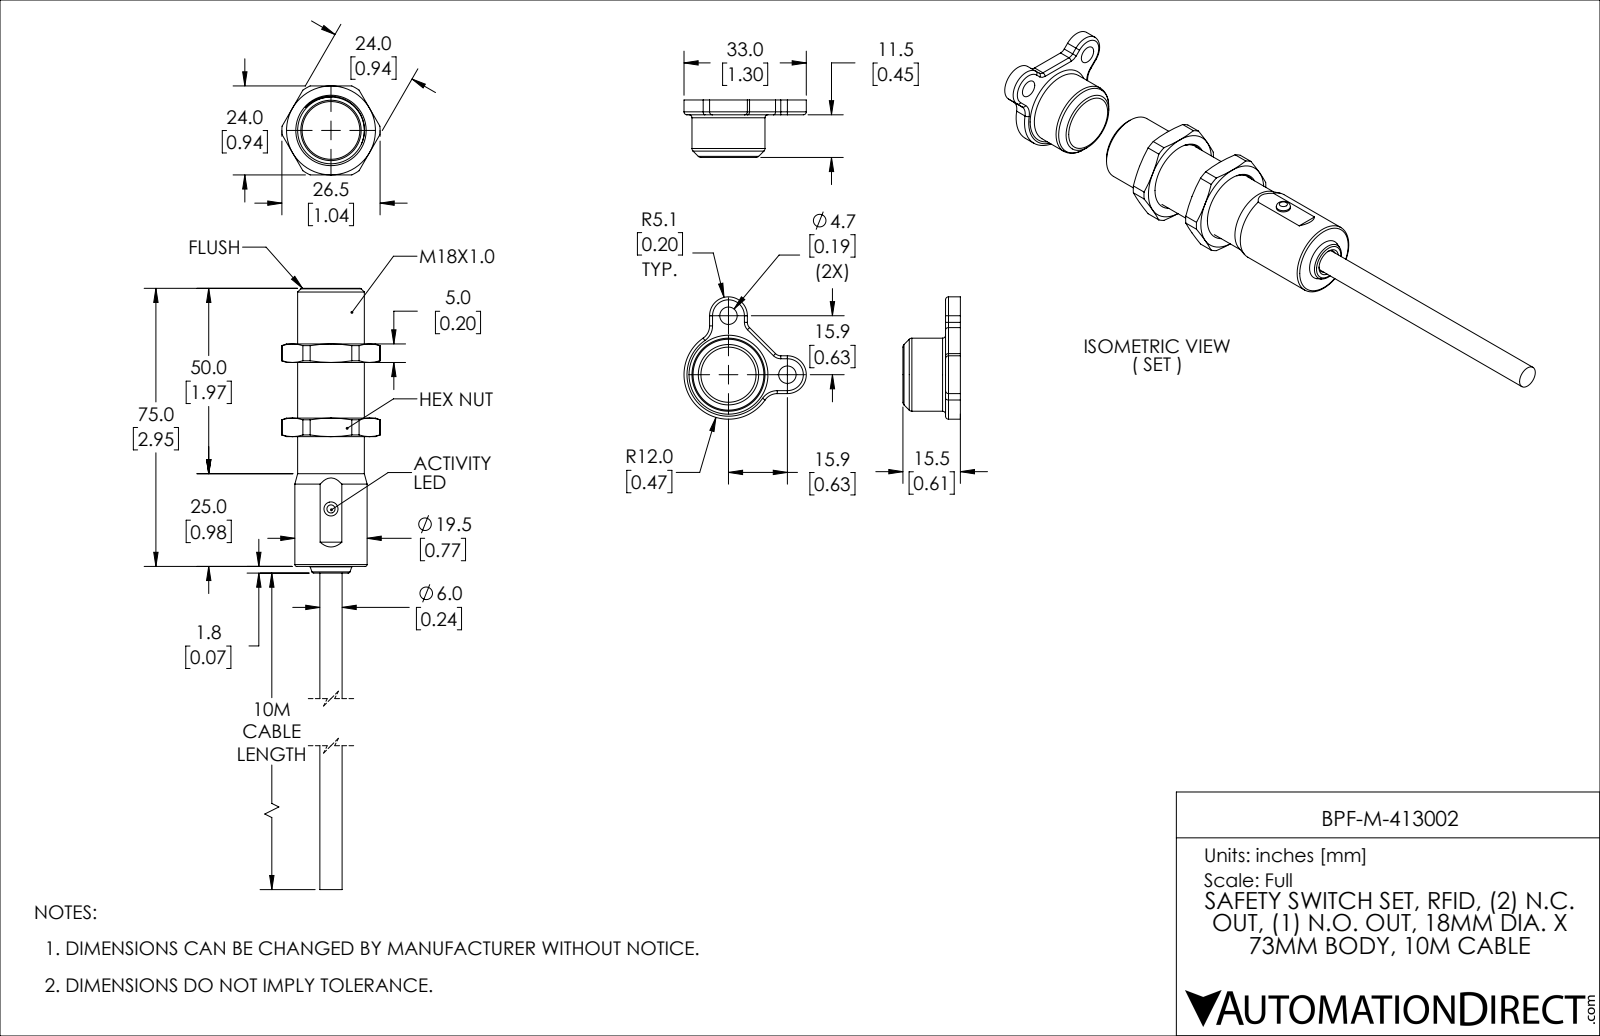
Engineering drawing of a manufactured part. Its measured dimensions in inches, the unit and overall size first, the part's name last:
Units: inches
Overall size (bounding box): 7.211 × 1.287 × 1.116
Round holes (diameter × count): ⌀0.098 ×4, ⌀0.185 ×2, ⌀0.055 ×1, ⌀0.079 ×1, ⌀0.118 ×1, ⌀0.252 ×1, ⌀0.449 ×1, ⌀0.528 ×1, ⌀0.63 ×1
Round bosses / shafts (diameter × count): ⌀0.776 ×1, ⌀0.768 ×1, ⌀0.709 ×1, ⌀0.646 ×1, ⌀0.622 ×1, ⌀0.543 ×1, ⌀0.236 ×1, ⌀0.15 ×1
Partial cylindrical surfaces — rounded edges, fillets, slot ends (radius × count): R0.031 ×5, R0.079 ×2, R0.157 ×2, R0.201 ×2, R0.472 ×1, R0.522 ×1
Main face-to-face distances: 0.591, 1.378, 0.787, 0.197, 1.575, 2.165, 0.945, 4.154, 0.059, 0.539
Hole centre spacings: 0.481, 0.191, 0.217, 0.626, 0.68, 0.191, 0.509, 0.698
Volume: 1.771 in³ · Surface area: 22.08 in²
Bodies: 8 solids, 178 faces (51 planar, 50 cylindrical, 77 other)
Part name (STEP PRODUCT): 413-BPF
STEP written by: SolidWorks 2019 (AUTOMOTIVE_DESIGN)
